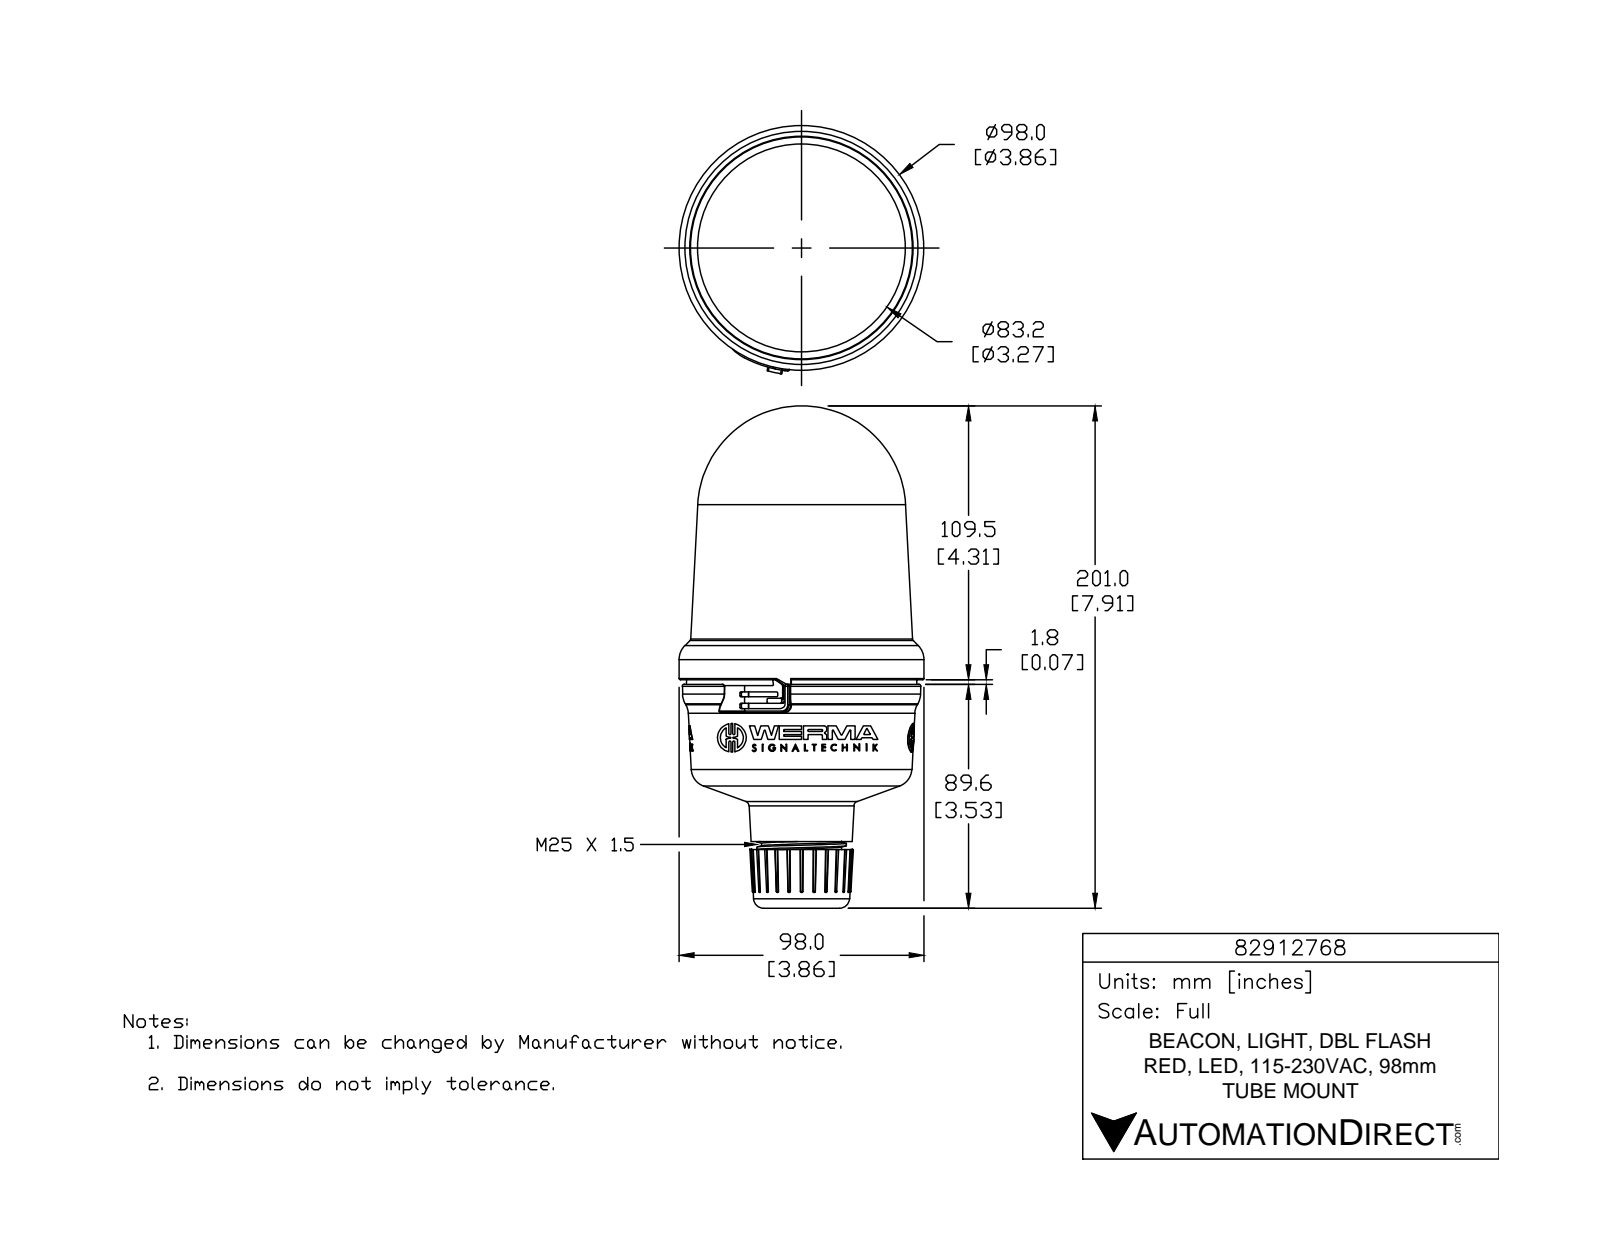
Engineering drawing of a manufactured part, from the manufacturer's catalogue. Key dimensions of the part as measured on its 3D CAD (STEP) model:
Part name (STEP PRODUCT): 82912768
STEP written by: SolidWorks 2015 (AUTOMOTIVE_DESIGN)
Units: inches
Bodies: 1 solid, 1006 faces (554 planar, 189 cylindrical, 263 other)
Overall size (bounding box): 7.914 × 3.912 × 3.858
Volume: 54.7 in³ · Surface area: 91.39 in²
Round holes (diameter × count): ⌀0.078 ×3, ⌀1.013 ×1, ⌀1.024 ×1
Round bosses / shafts (diameter × count): ⌀0.452 ×3, ⌀0.113 ×3, ⌀3.858 ×1, ⌀1.409 ×1, ⌀1.261 ×1
Partial cylindrical surfaces — rounded edges, fillets, slot ends (radius × count): R0.02 ×12, R0.007 ×9, R0.007 ×6, R0.016 ×6, R0.016 ×6, R0.016 ×6, R0.262 ×6, R0.006 ×3
Main face-to-face distances: 2.214, 0.462, 2.676, 0.335, 0.127, 2.548, 2.603, 2.476, 2.141, 0.073
